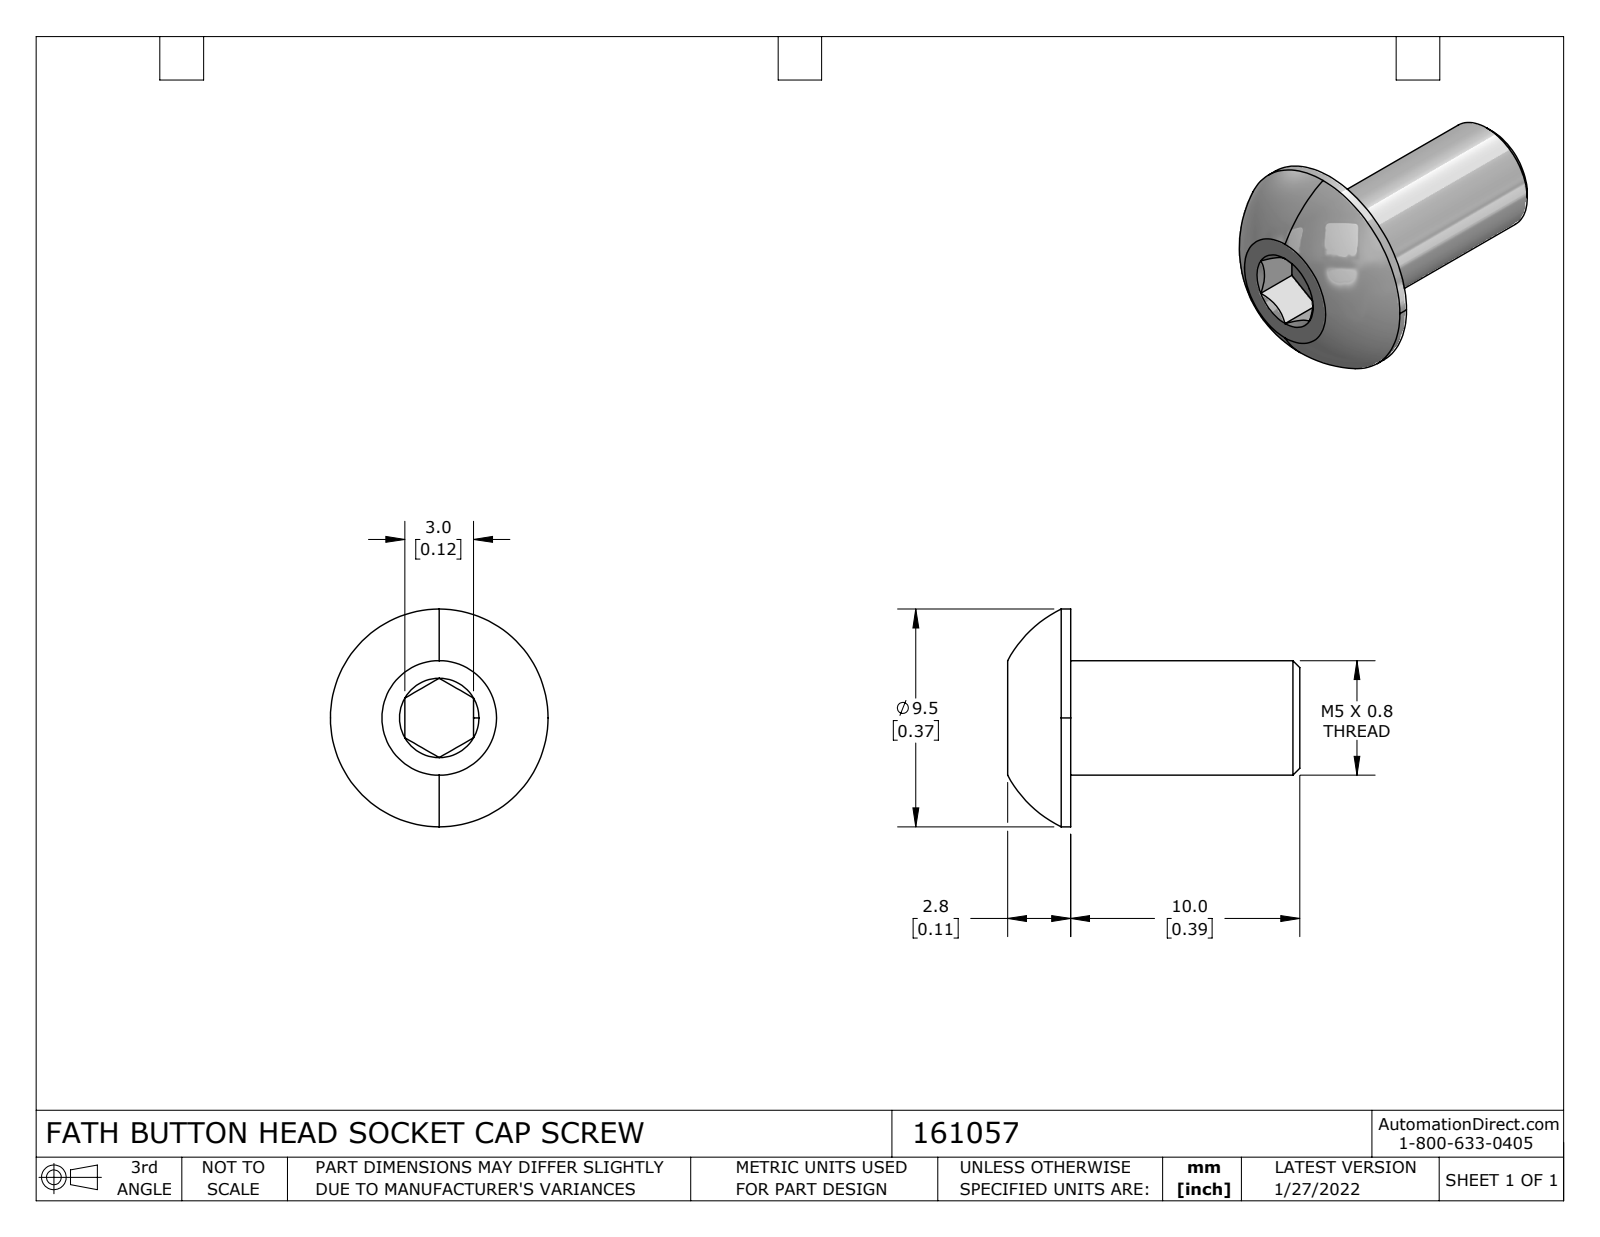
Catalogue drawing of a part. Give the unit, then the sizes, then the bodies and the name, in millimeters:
Units: millimetres
Overall size (bounding box): 12.75 × 9.5 × 9.5
Round bosses / shafts (diameter × count): ⌀9.5 ×1, ⌀5 ×1
Main face-to-face distances: 10, 12.75, 2.75, 3, 10.82, 0.82, 1.93
Volume: 322 mm³ · Surface area: 354 mm²
Bodies: 1 solid, 25 faces (10 planar, 4 cylindrical, 11 other)
Part name (STEP PRODUCT): 161057
STEP written by: SolidWorks 2021 (CONFIG_CONTROL_DESIGN)
